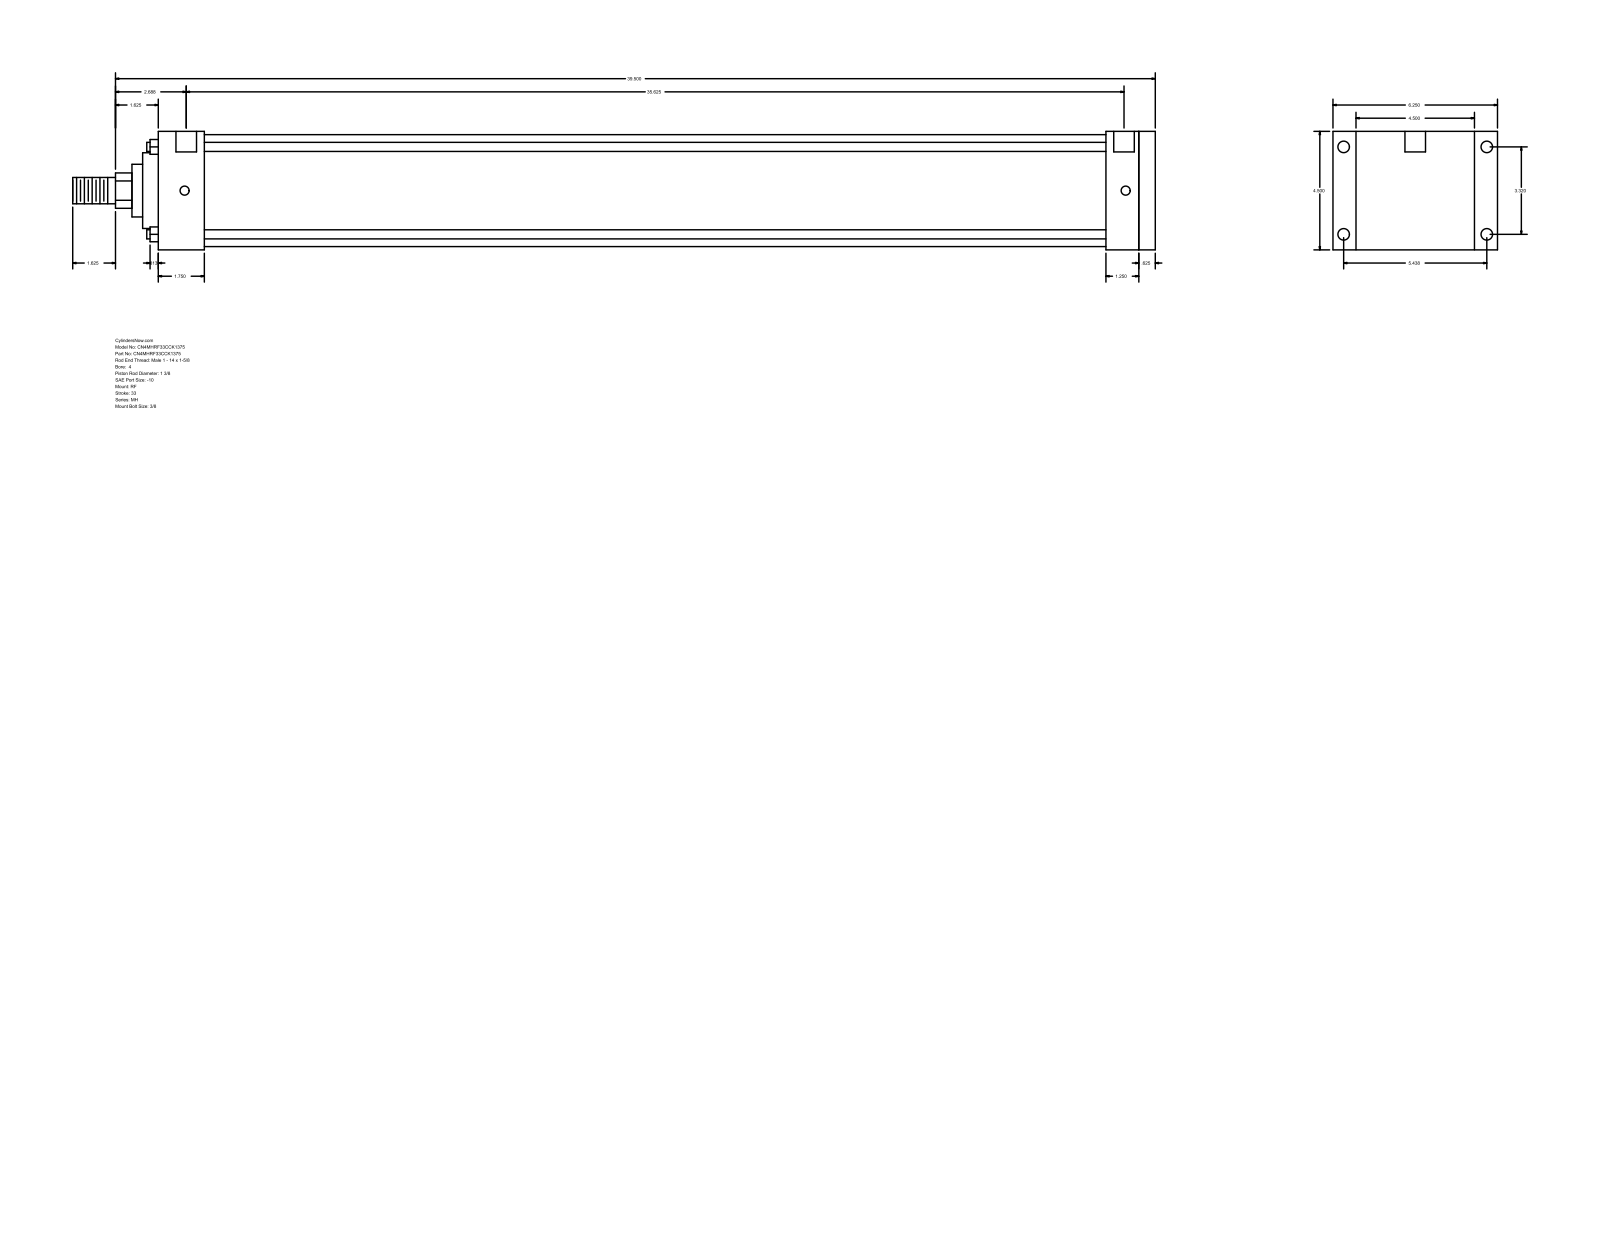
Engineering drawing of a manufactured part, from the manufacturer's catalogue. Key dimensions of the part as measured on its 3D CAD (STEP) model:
Part name (STEP PRODUCT): MH_RF__0400_1.375
STEP written by: GSSL Pune (CONFIG_CONTROL_DESIGN)
Units: millimetres
Bodies: 0 solids, 94 faces (65 planar, 29 cylindrical, 0 other)
Overall size (bounding box): 1044.58 × 158.75 × 114.3
Round holes (diameter × count): ⌀8.73 ×4, ⌀11.13 ×4, ⌀19.84 ×2
Round bosses / shafts (diameter × count): ⌀8.76 ×4, ⌀107.95 ×1, ⌀73.03 ×1, ⌀50.8 ×1, ⌀34.92 ×1, ⌀25.4 ×1
Partial cylindrical surfaces — rounded edges, fillets, slot ends (radius × count): R17.06 ×1
Main face-to-face distances: 114.3, 962.03, 15.88, 946.15, 44.45, 901.7, 917.58, 914.4, 869.95, 31.75
Hole centre spacings: 1.59, 84.32, 138.12, 161.82, 906.47, 908.06, 904.88
